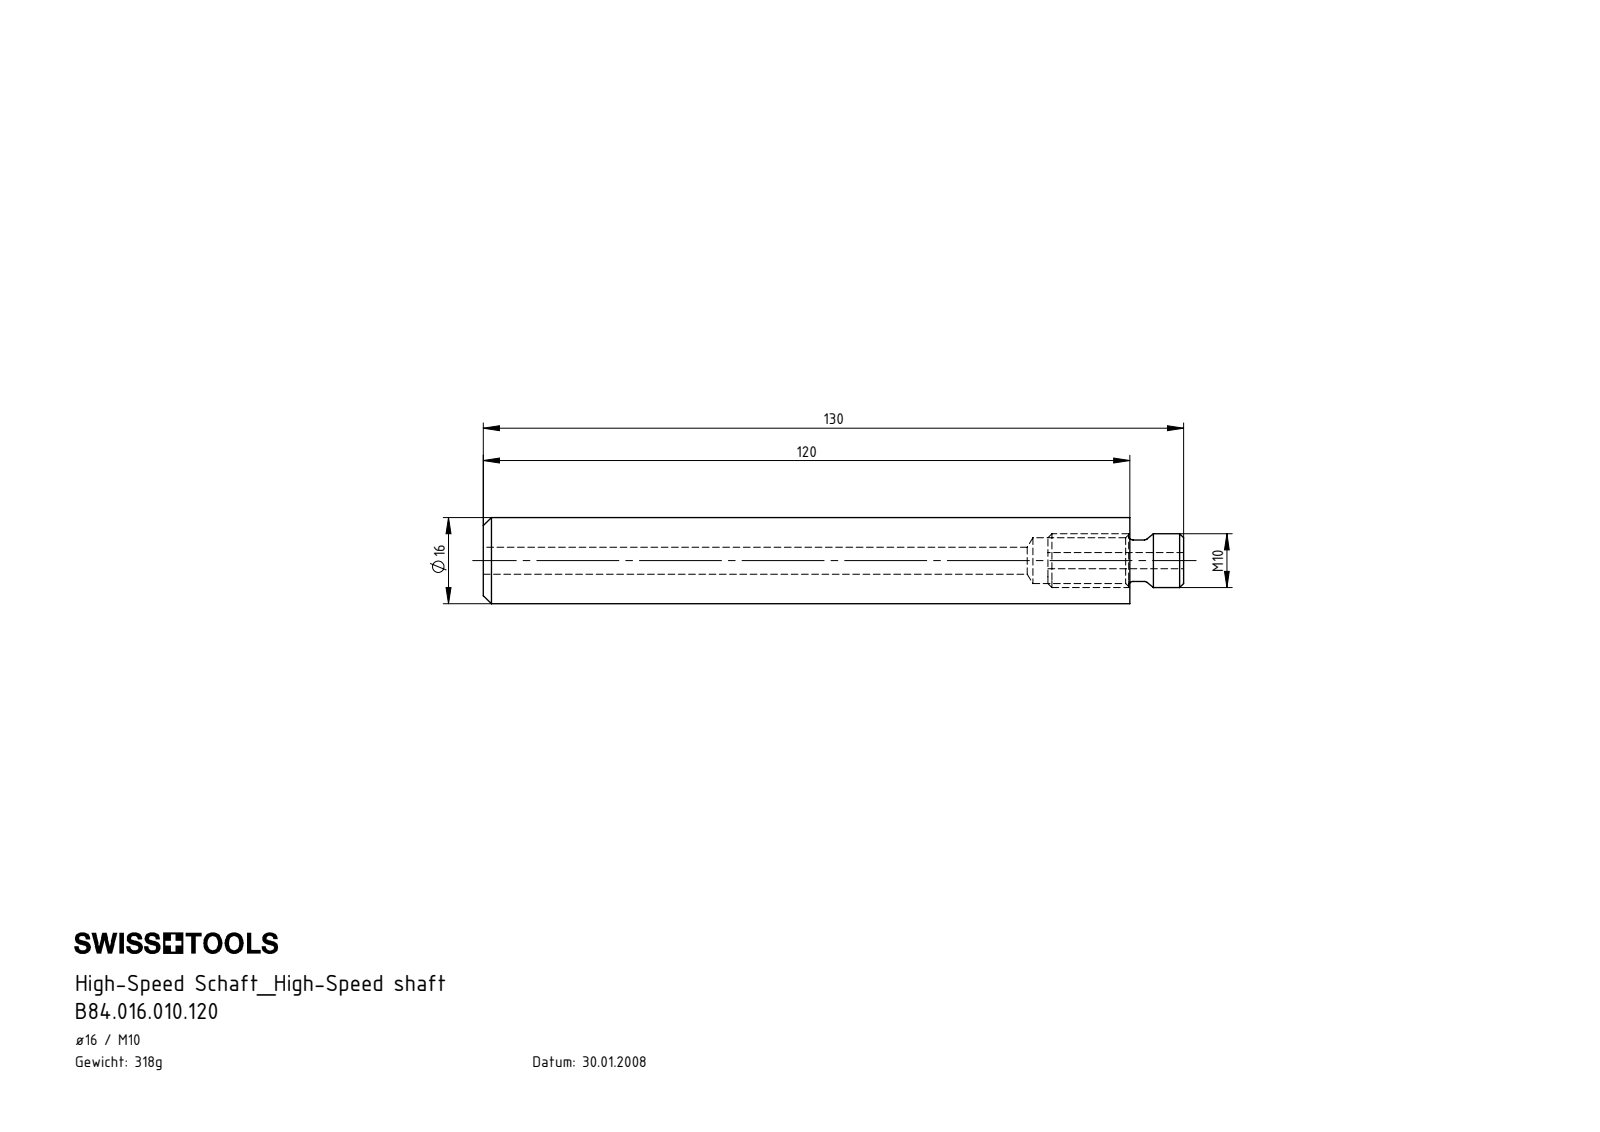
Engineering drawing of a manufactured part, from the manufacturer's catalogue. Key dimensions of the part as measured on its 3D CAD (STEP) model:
Part name (STEP PRODUCT): HM1-BG1.010.025_A; U16-HS0.K01.120_A; HM1-U16.001.120_A
STEP written by: SolidWorks 2012 (AUTOMOTIVE_DESIGN)
Units: millimetres
Bodies: 2 solids, 35 faces (5 planar, 14 cylindrical, 16 other)
Overall size (bounding box): 130 × 16 × 16
Volume: 22 687 mm³ · Surface area: 9 559 mm²
Round holes (diameter × count): ⌀3 ×1, ⌀5 ×1, ⌀8.5 ×1
Round bosses / shafts (diameter × count): ⌀16 ×1, ⌀10 ×1, ⌀7.7 ×1
Main face-to-face distances: 120, 130, 10, 104.8, 15.2, 25.2, 119.8, 15, 10.2
